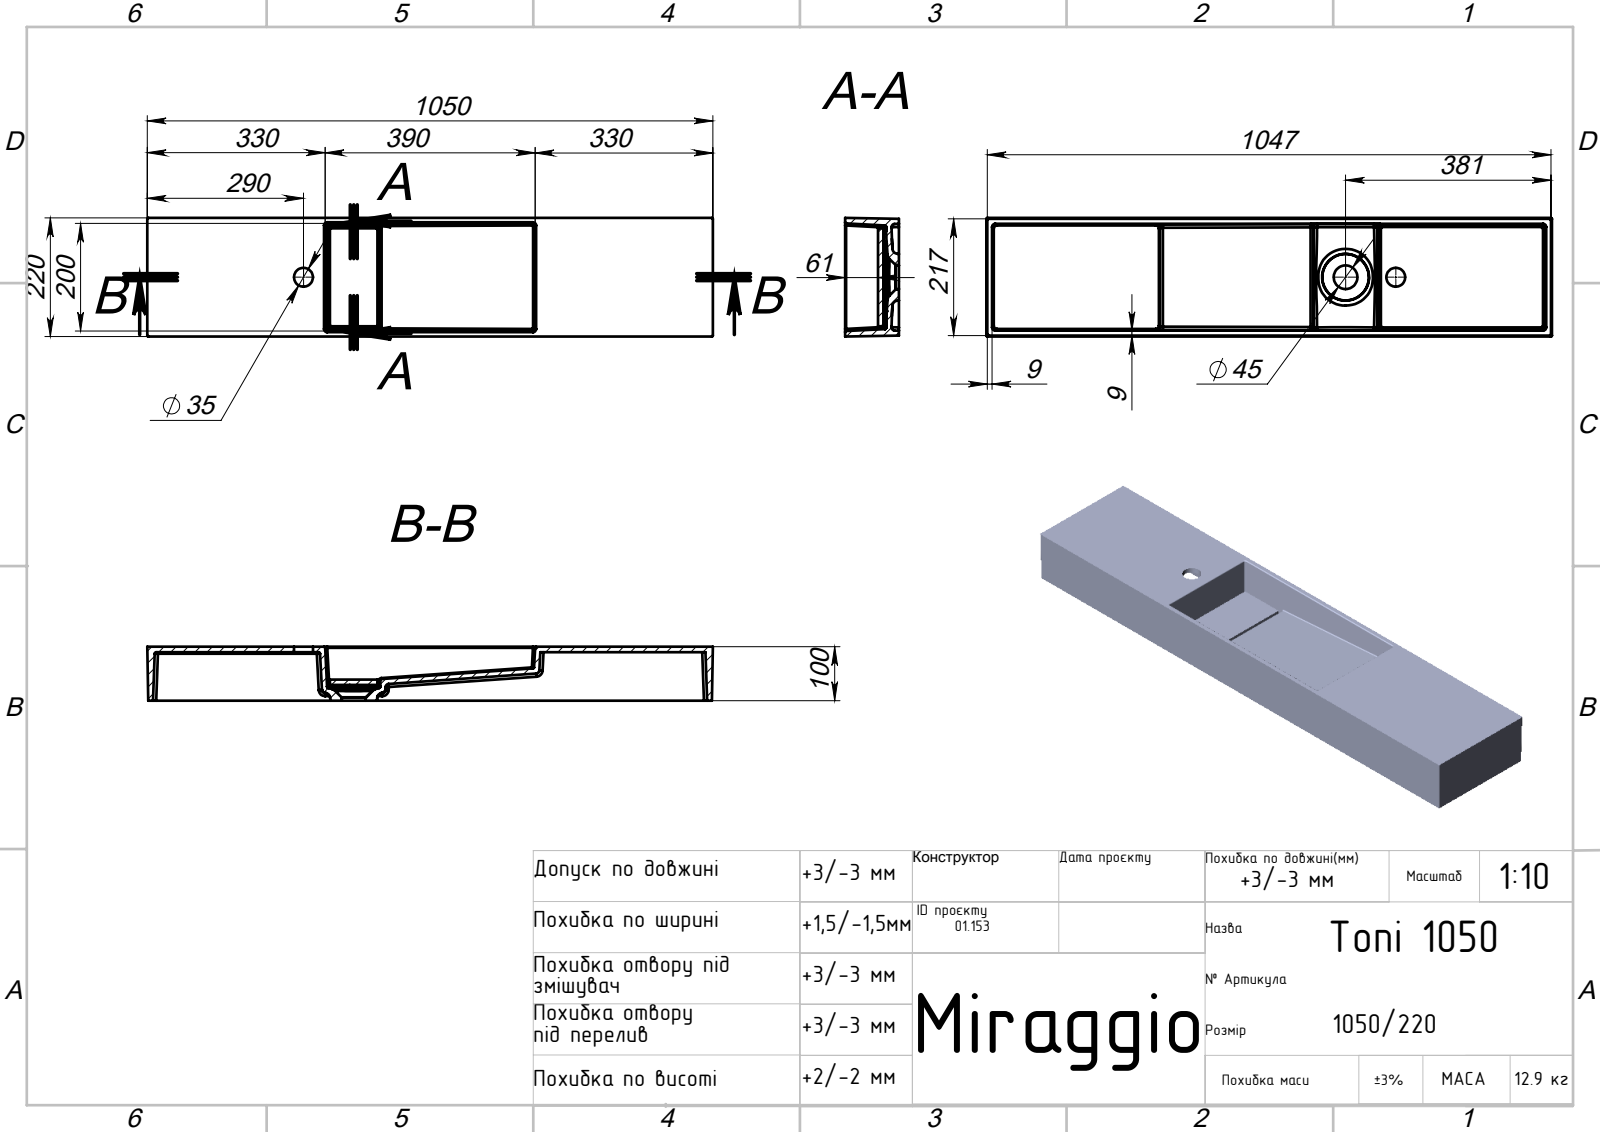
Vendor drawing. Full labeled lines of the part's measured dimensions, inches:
Part name (STEP PRODUCT): Toni 1050
STEP written by: SolidWorks 2020 (AUTOMOTIVE_DESIGN)
Units: inches
Bodies: 2 solids, 128 faces (32 planar, 46 cylindrical, 50 other)
Overall size (bounding box): 41.339 × 8.661 × 3.937
Volume: 318.8 in³ · Surface area: 1 549 in²
Round holes (diameter × count): ⌀0.394 ×4, ⌀1.378 ×1, ⌀1.772 ×1
Partial cylindrical surfaces — rounded edges, fillets, slot ends (radius × count): R0.079 ×16, R0.236 ×14, R0.157 ×6, R0.118 ×4
Main face-to-face distances: 0.394, 2.402, 3.543, 3.937, 1.142, 2.795, 1.535, 2.008, 0.394, 11.159
Hole centre spacings: 5.906, 31.358, 3.667, 25.453, 37.264
